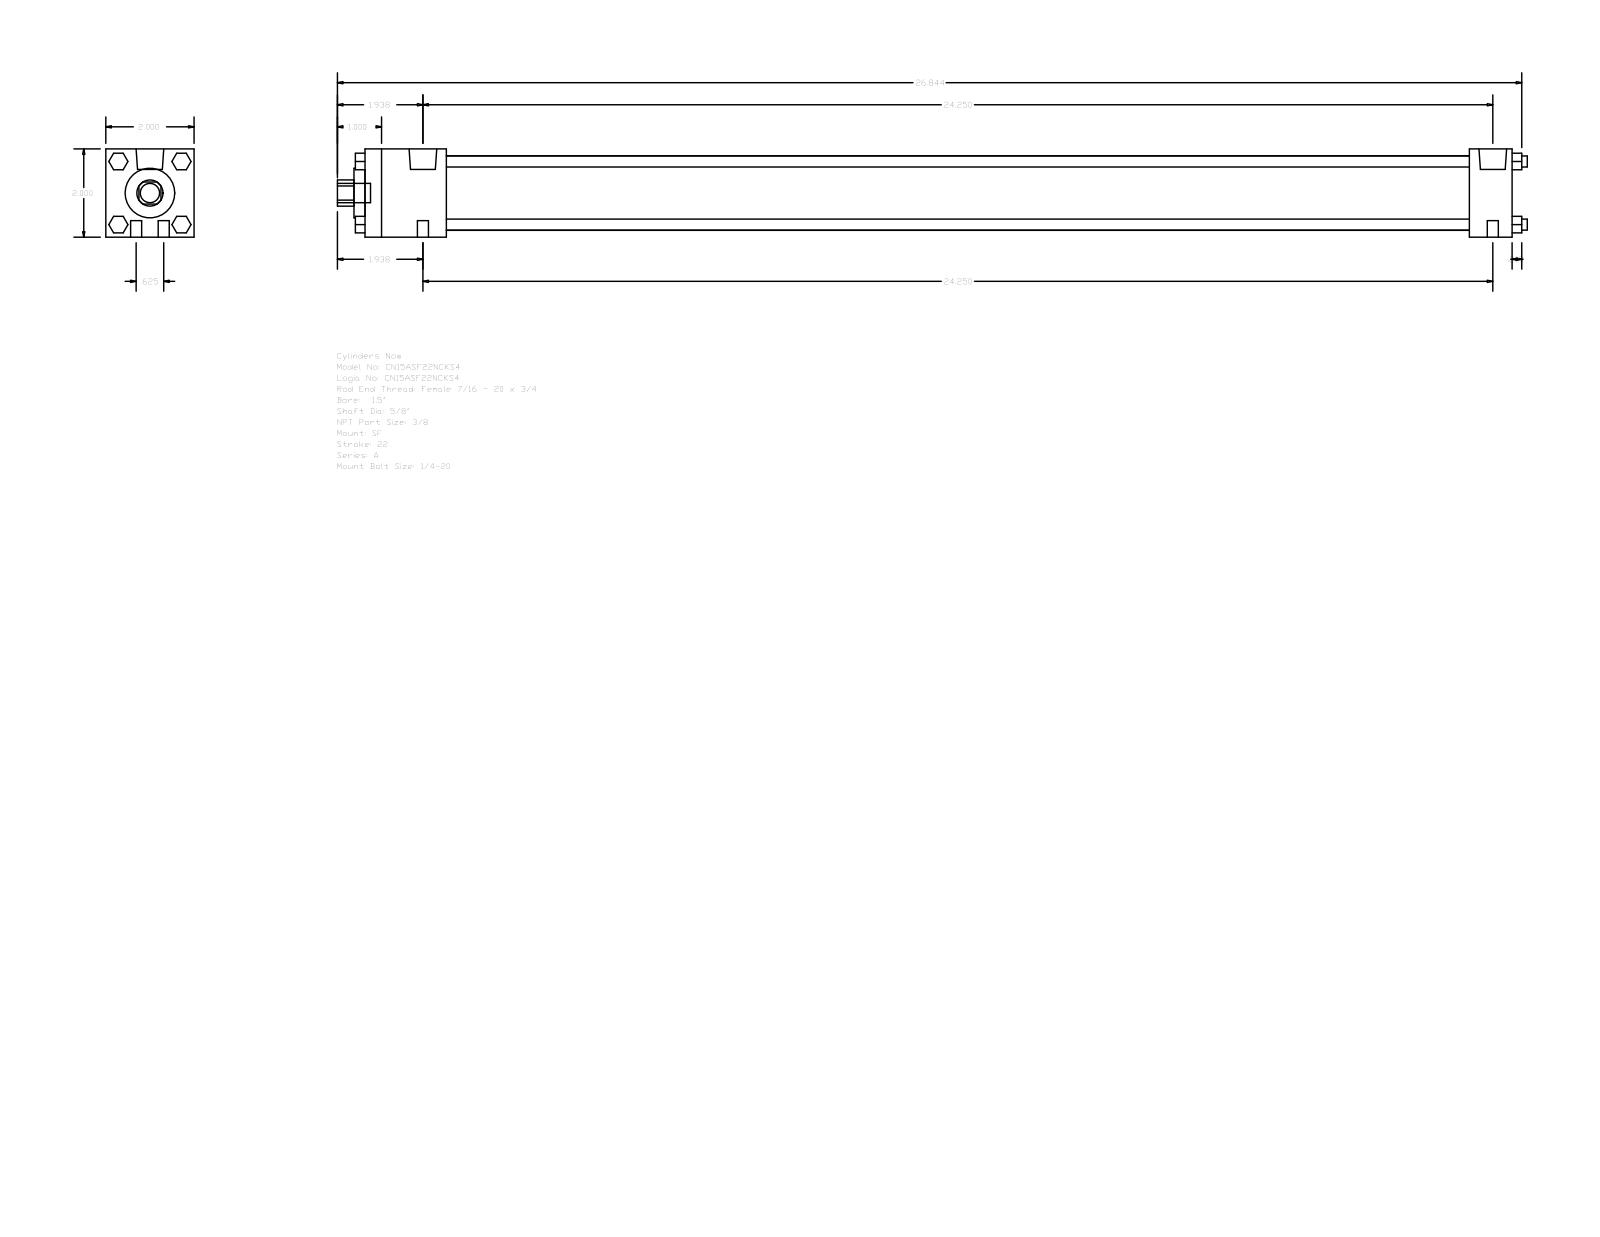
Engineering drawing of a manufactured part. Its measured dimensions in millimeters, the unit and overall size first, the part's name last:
Units: millimetres
Overall size (bounding box): 685.01 × 50.8 × 50.8
Round holes (diameter × count): ⌀15.88 ×1, ⌀28.57 ×1, ⌀42.93 ×1
Round bosses / shafts (diameter × count): ⌀6.35 ×8, ⌀15.93 ×2, ⌀5.56 ×2, ⌀11.11 ×1
Partial cylindrical surfaces — rounded edges, fillets, slot ends (radius × count): R7.54 ×1
Main face-to-face distances: 50.8, 660.39, 46.83, 635.79, 588.96, 613.56, 24.6, 9.52, 6.35, 53.18
Bodies: 0 solids, 124 faces (94 planar, 30 cylindrical, 0 other)
Part name (STEP PRODUCT): A_SF__0150_0.625
STEP written by: GSSL Pune (CONFIG_CONTROL_DESIGN)
